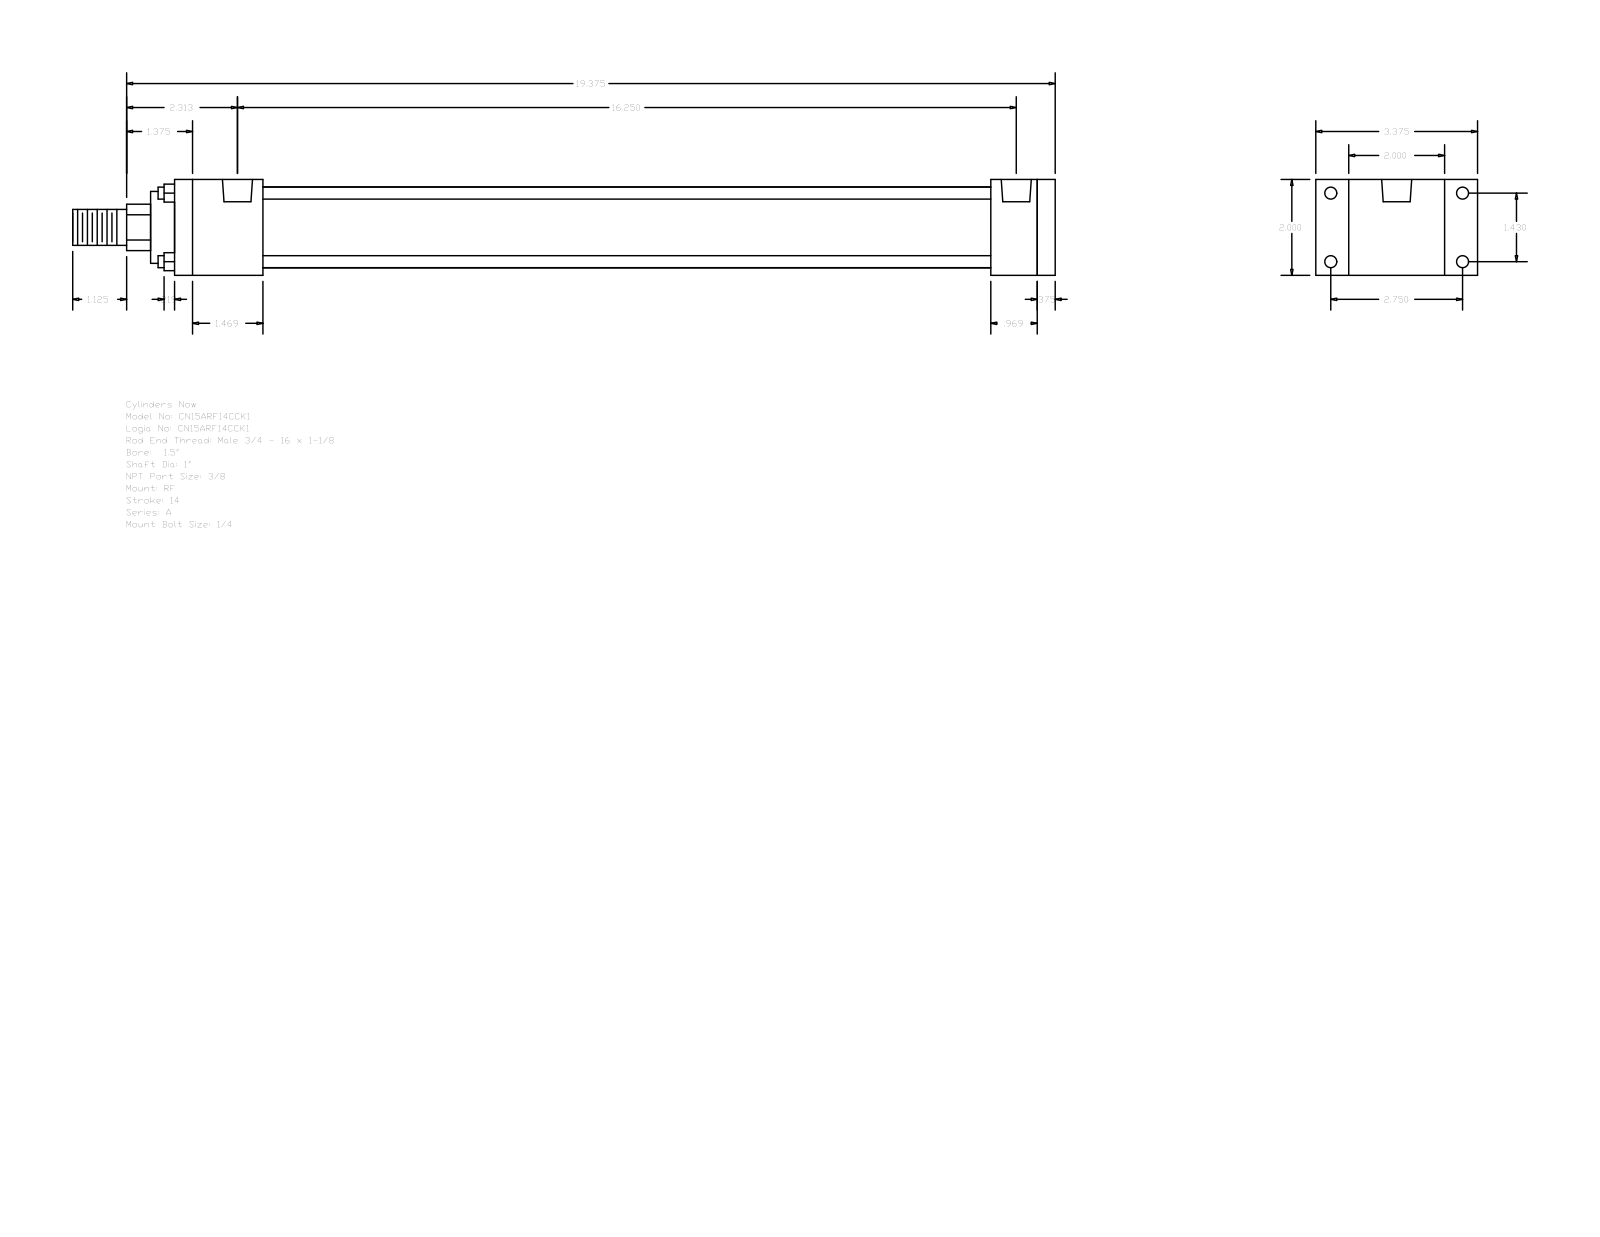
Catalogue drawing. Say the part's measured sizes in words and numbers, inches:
The part is named "A_RF__0150_1". Its 3-D file was written by "GSSL Pune (CONFIG_CONTROL_DESIGN)". It is 0 solids with 92 faces: 64 planar, 28 cylindrical and 0 other. Overall it measures 20.5 by 3.375 by 2 inches. Round holes: 4 of diameter 0.219, 4 of diameter 0.25, 2 of diameter 0.627. Round bosses or shafts: 4 of diameter 0.25, 1 of diameter 1.69, 1 of diameter 1.5, 1 of diameter 1, 1 of diameter 0.75. Partial cylindrical surfaces (rounded edges, fillets, slot ends): 1 of radius 0.484. The main face-to-face distances are 2, 0.375, 18, 18.375, 17.031, 0.969, 1.344, 1.844, 15.187, 16.156. The hole center spacings are 0.156, 1.43, 2.75, 3.099, 15.937, 16.094, 16.25.
